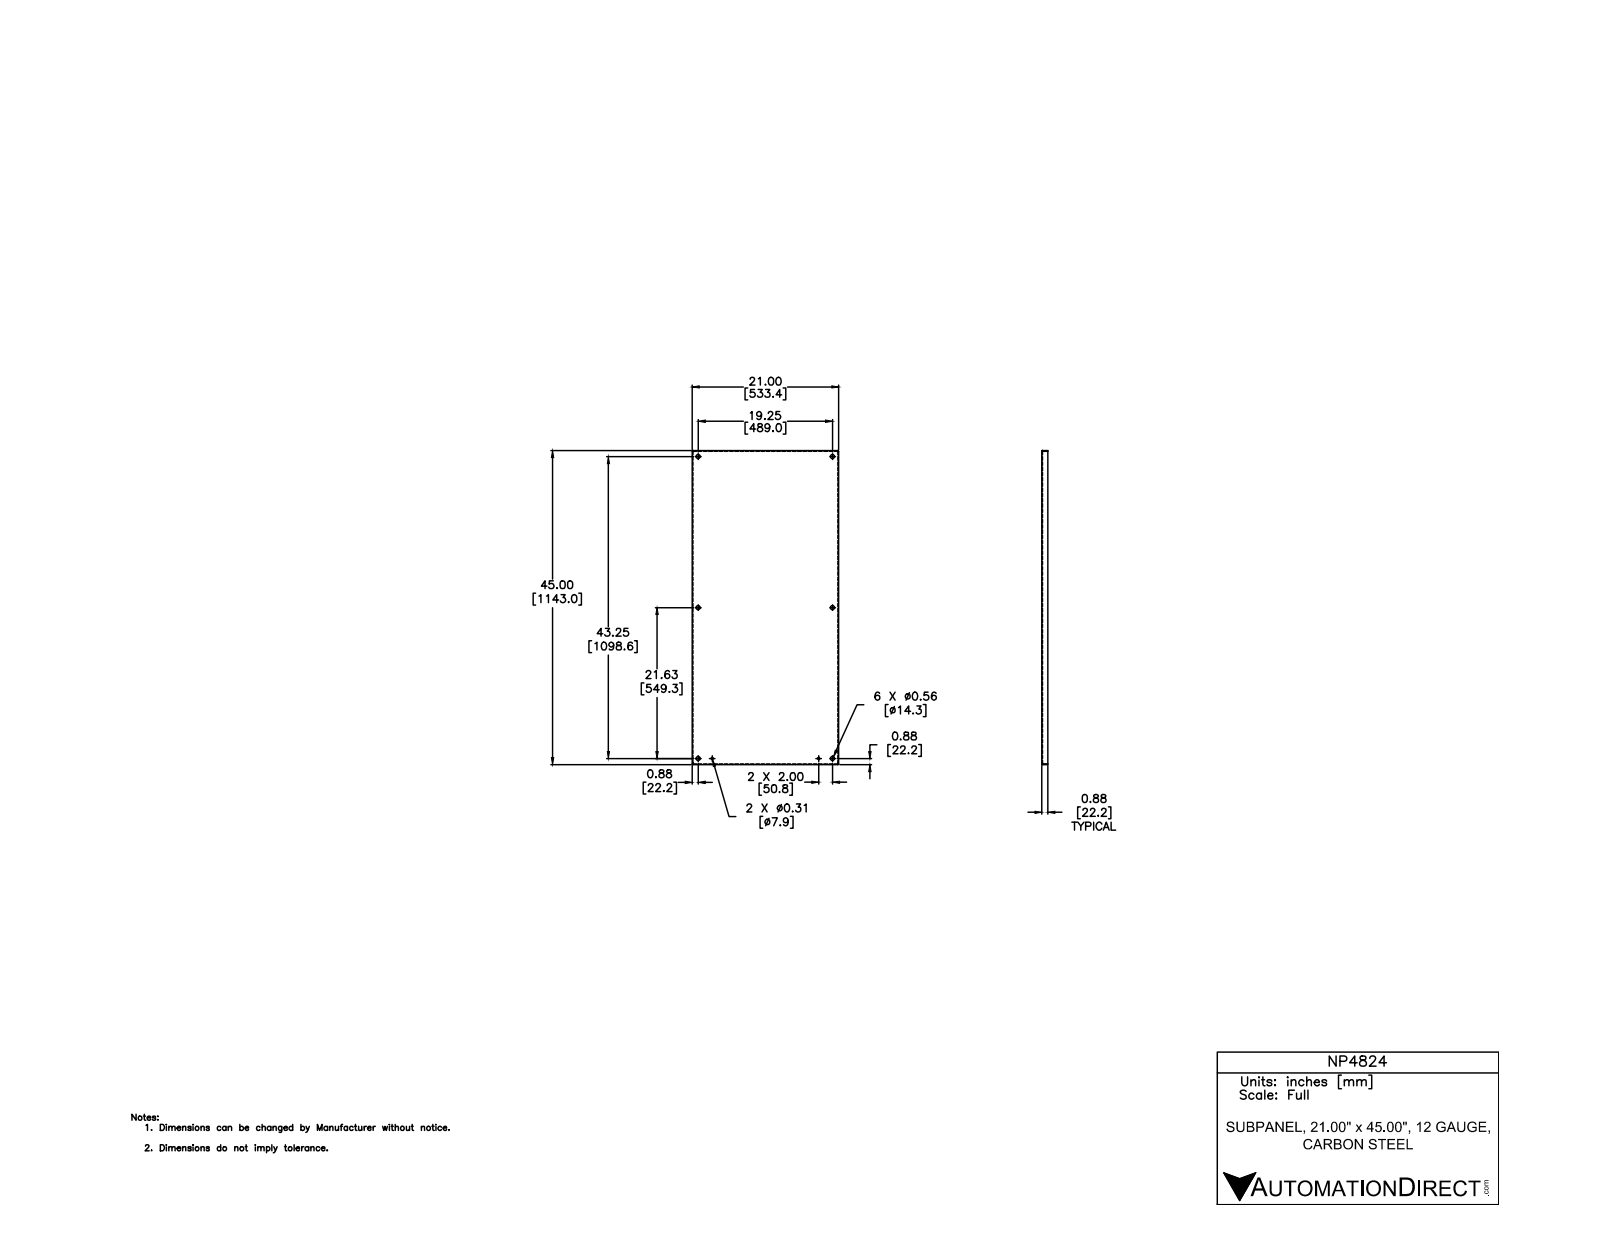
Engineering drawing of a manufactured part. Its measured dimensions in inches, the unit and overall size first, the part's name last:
Units: inches
Overall size (bounding box): 45 × 21 × 0.875
Round holes (diameter × count): ⌀0.563 ×6, ⌀0.312 ×2
Partial cylindrical surfaces — rounded edges, fillets, slot ends (radius × count): R0.031 ×4, R0.125 ×4
Main face-to-face distances: 0.094, 20.906, 21, 20.813, 44.906, 44.813, 45, 0.781, 0.875, 0.105
Hole centre spacings: 21.625, 28.952, 19.25, 43.25, 46.563, 47.341, 2, 2
Volume: 97.63 in³ · Surface area: 2 097 in²
Bodies: 1 solid, 46 faces (22 planar, 16 cylindrical, 8 other)
Part name (STEP PRODUCT): NP4824
STEP written by: Autodesk Inventor 2012 (AUTOMOTIVE_DESIGN)
